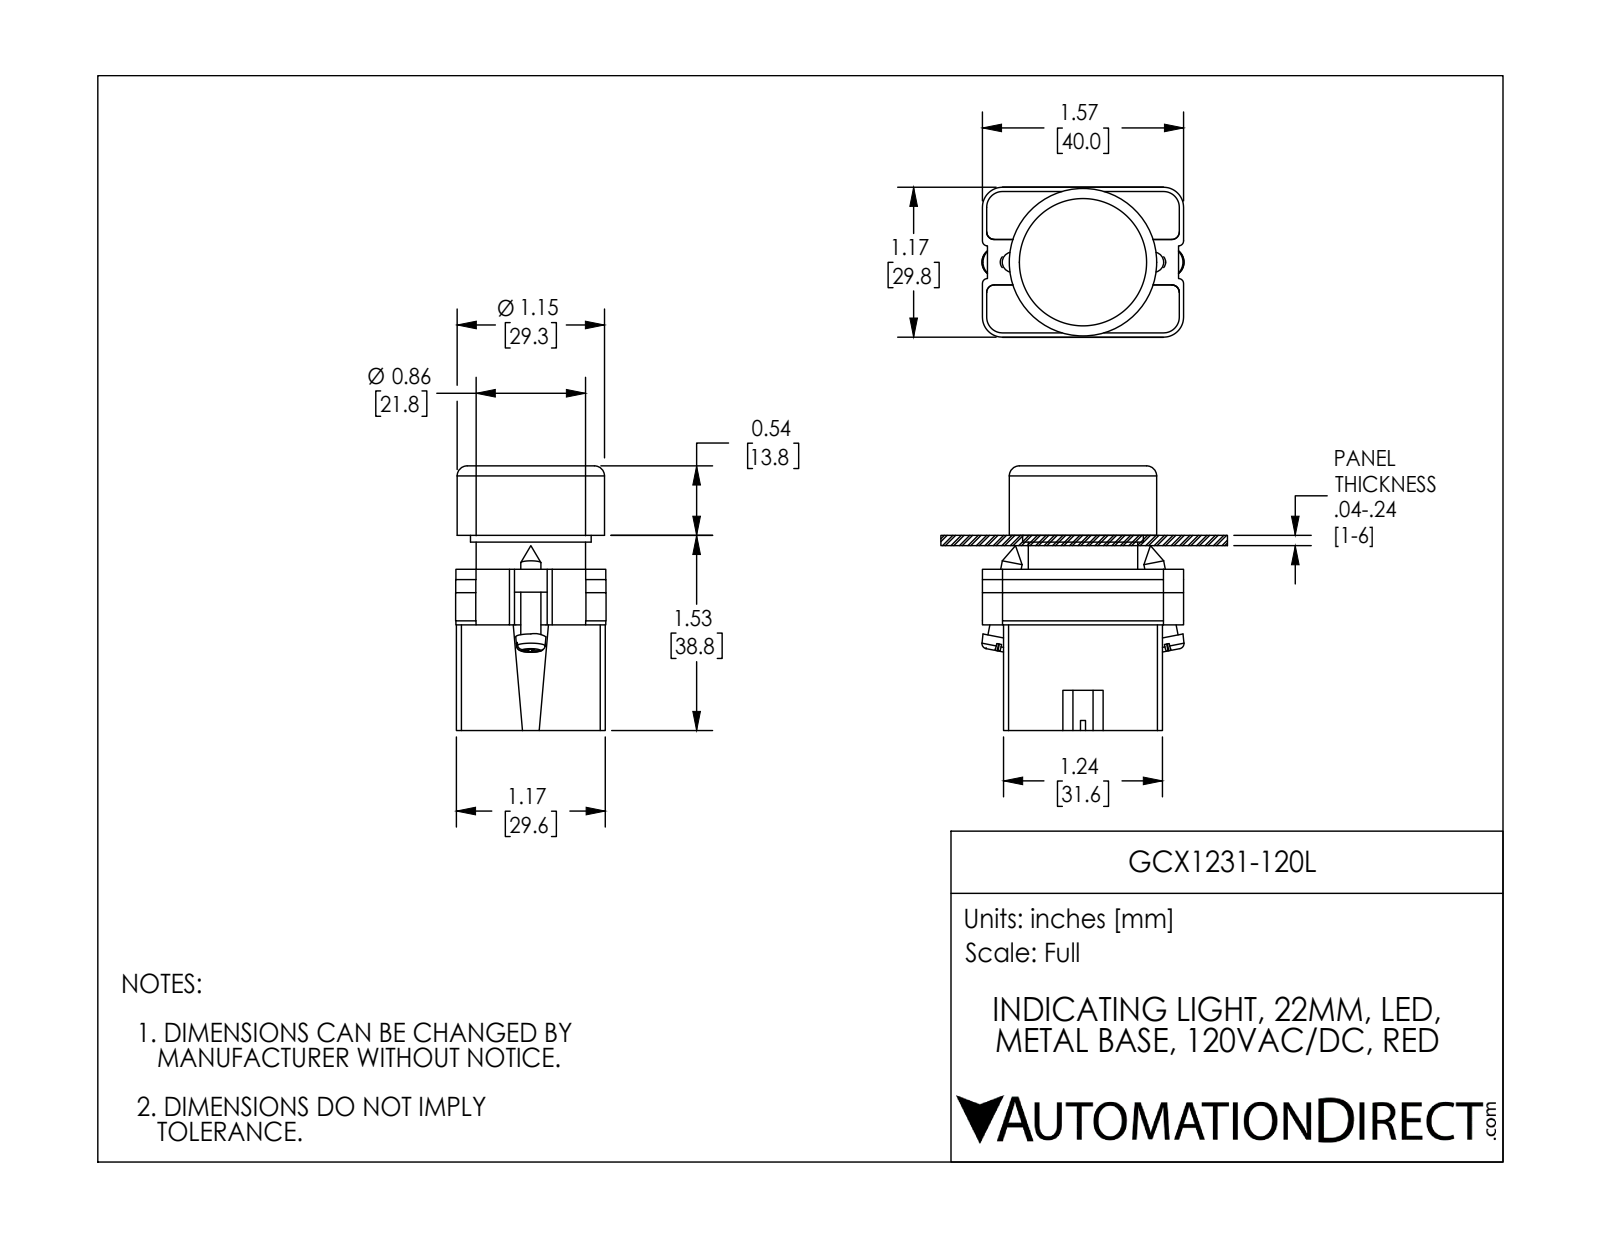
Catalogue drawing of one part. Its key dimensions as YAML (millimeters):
part_name: "ECX1050; GCX1231L OPERATOR; GCX1231-120L; ecx1029"
step_written_by: "SolidWorks 2016 (AUTOMOTIVE_DESIGN)"
units: millimeters
bodies: {solids: 7, faces: 339, planar: 178, cylindrical: 134, other: 27}
overall_size: [52.6, 40.2, 29.9]
volume: 37170
surface_area: 20120
round_holes:
  - {diameter: 3.1, count: 2}
  - {diameter: 3.3, count: 2}
  - {diameter: 5, count: 1}
  - {diameter: 11.9, count: 1}
  - {diameter: 21.6, count: 1}
  - {diameter: 22.3, count: 1}
  - {diameter: 22.6, count: 1}
  - {diameter: 28, count: 1}
round_bosses_or_shafts:
  - {diameter: 4, count: 4}
  - {diameter: 29.3, count: 1}
  - {diameter: 27.7, count: 1}
  - {diameter: 24, count: 1}
  - {diameter: 21.7, count: 1}
  - {diameter: 19.8, count: 1}
  - {diameter: 12.8, count: 1}
partial_cylinders:
  - {radius: 1.5, count: 24}
  - {radius: 1, count: 12}
  - {radius: 3.1, count: 12}
  - {radius: 4, count: 12}
  - {radius: 1, count: 8}
  - {radius: 3.3, count: 2}
  - {radius: 10, count: 1}
  - {radius: 10.1, count: 1}
face_to_face_distances: [21.8, 31.6, 21, 42.8, 28.9, 0.8, 49.9, 7, 0.8, 29.6]
